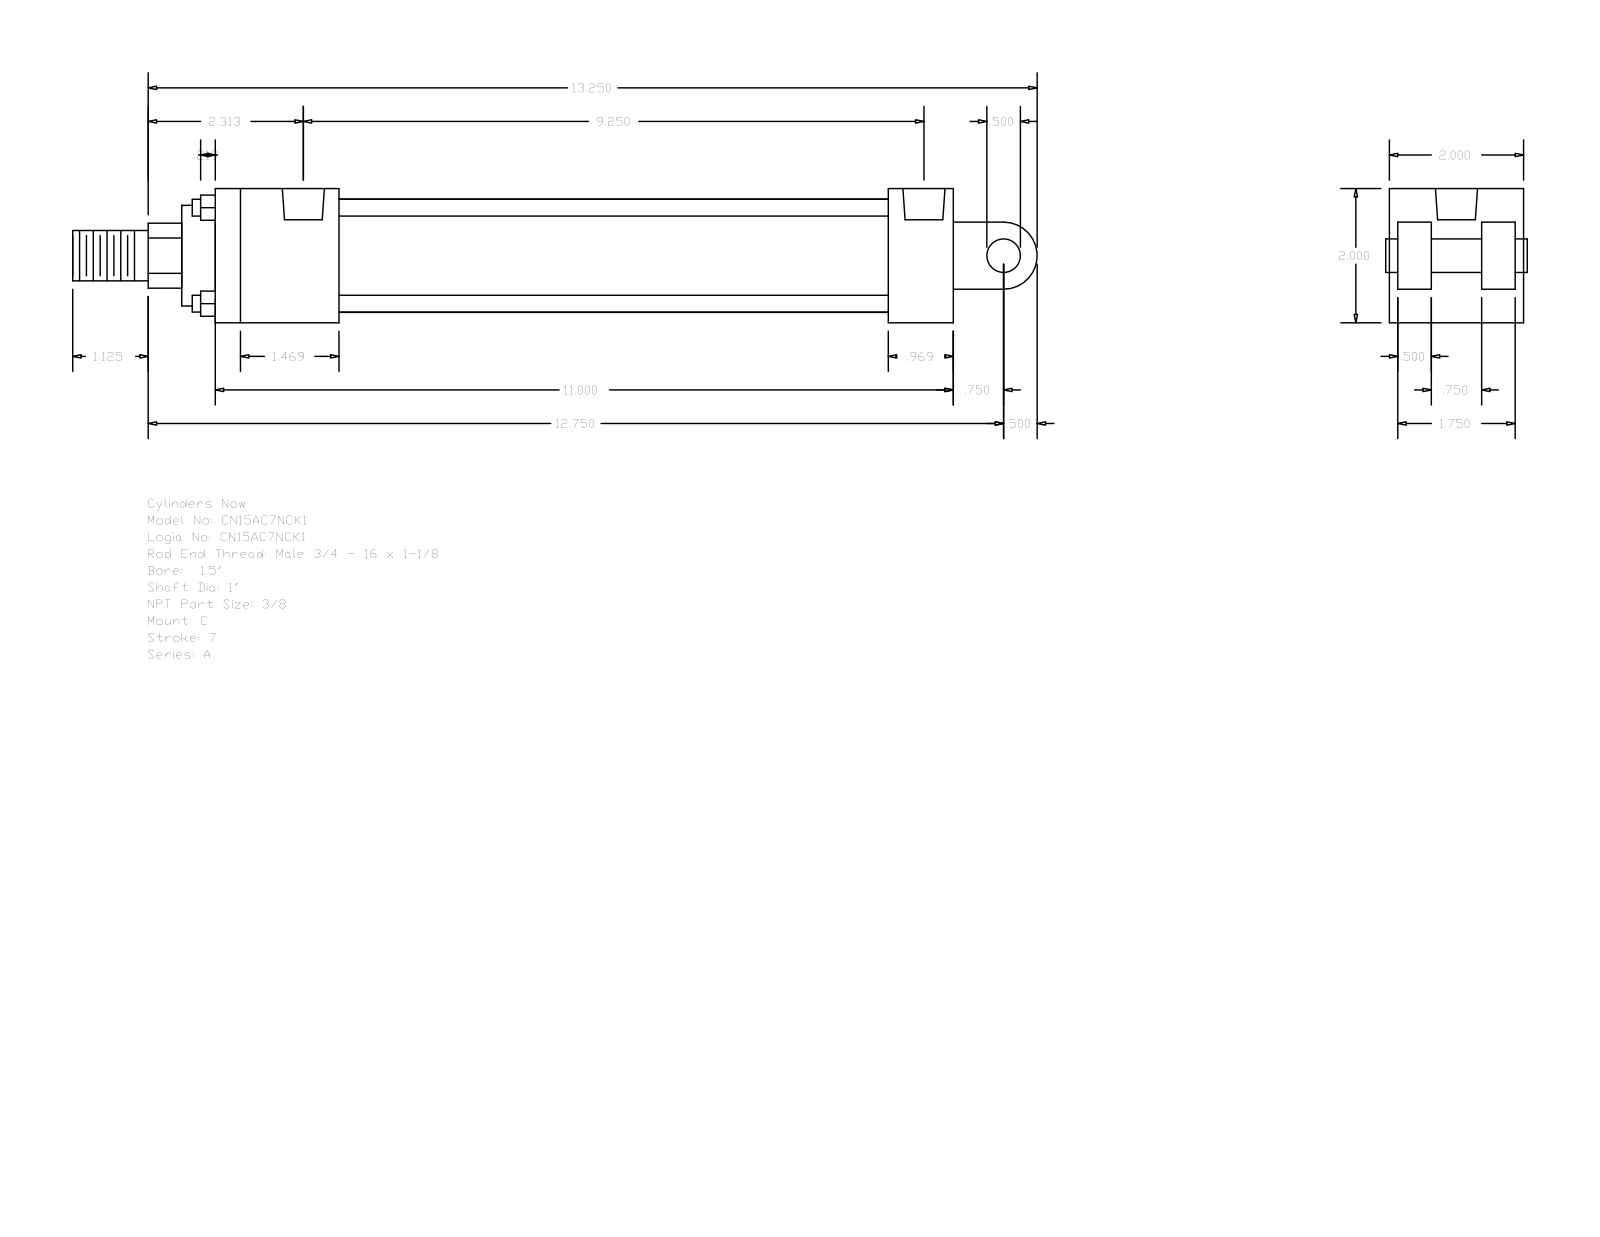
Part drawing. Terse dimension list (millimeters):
name: A_C__0150_1
written by: GSSL Pune (CONFIG_CONTROL_DESIGN)
unit: mm
bodies: 0 solids, 99 faces (70 planar, 29 cylindrical, 0 other)
size: 365.12 × 50.8 × 50.8
holes: 4× ⌀5.56, 2× ⌀15.93
bosses: 4× ⌀6.35, 1× ⌀42.93, 1× ⌀38.1, 1× ⌀25.4, 1× ⌀19.05, 1× ⌀12.7
rounds: 1× R12.29, 1× R12.7
face distances: 50.8, 12.7, 3.17, 15.87, 34.93, 47.63, 31.76, 279.4, 38.1, 254.79
hole spacings: 3.97, 227.01, 230.98, 234.95
